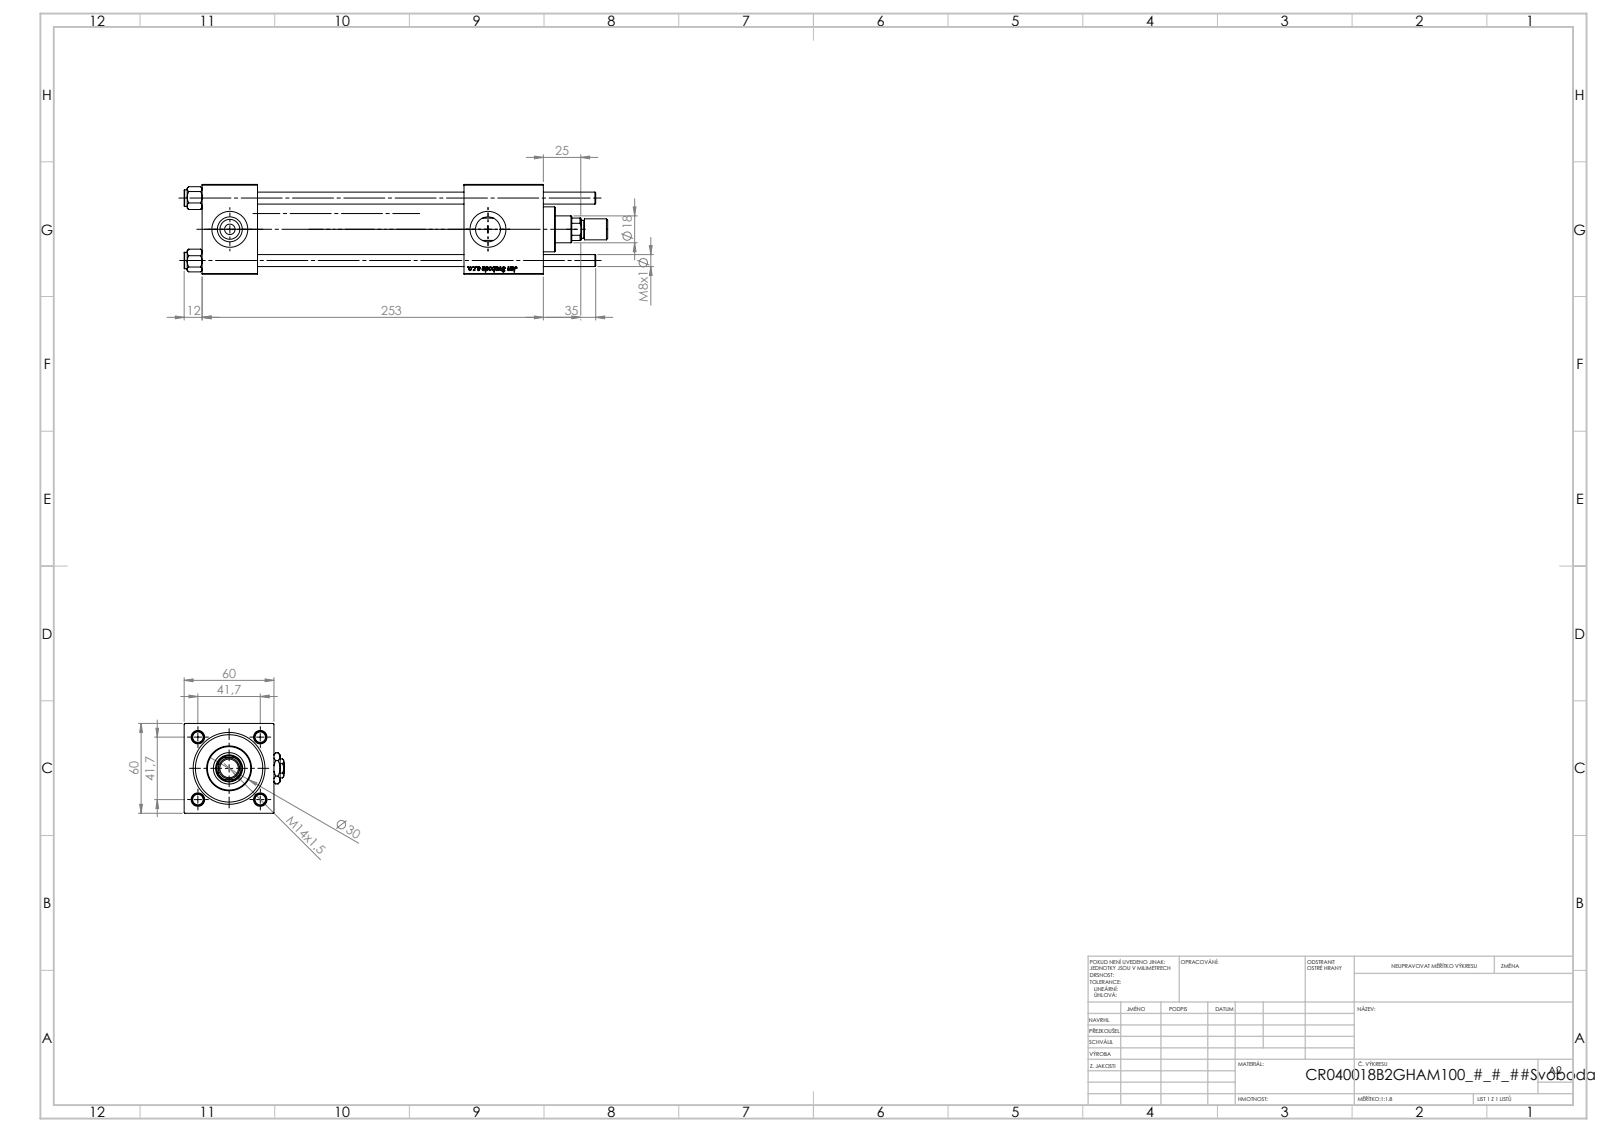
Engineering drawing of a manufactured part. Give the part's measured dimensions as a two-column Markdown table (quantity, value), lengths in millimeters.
| quantity | value |
| --- | --- |
| part name | Zatka_pro_OIL_PORT; V215_VC_A; V215CR_B_TYCINKA; V215CR_B-1 (+3 more) |
| STEP written by | SolidWorks 2019 (CONFIG_CONTROL_DESIGN) |
| units | millimeters |
| bodies | 13 solids, 1225 faces (461 planar, 88 cylindrical, 676 other) |
| overall size | 283 × 67 × 60 |
| volume | 484 139 mm³ |
| surface area | 150 713 mm² |
| round holes (diameter × count) | 8 × 4, 7 × 2, 16.66 × 2, 24 × 2, 8.5 × 1, 18 × 1, 21 × 1, 31 × 1, 40 × 1, 45 × 1 |
| round bosses / shafts (diameter × count) | 11 × 4, 46 × 1, 30 × 1, 14 × 1, 12 × 1 |
| partial cylindrical surfaces (radius × count) | 8.5 × 1 |
| main face-to-face distances | 60, 37, 228, 191, 53, 175, 138, 199.3, 162.3, 24.3 |
| hole center spacings | 29.49, 41.7, 58.97, 172.5 |
